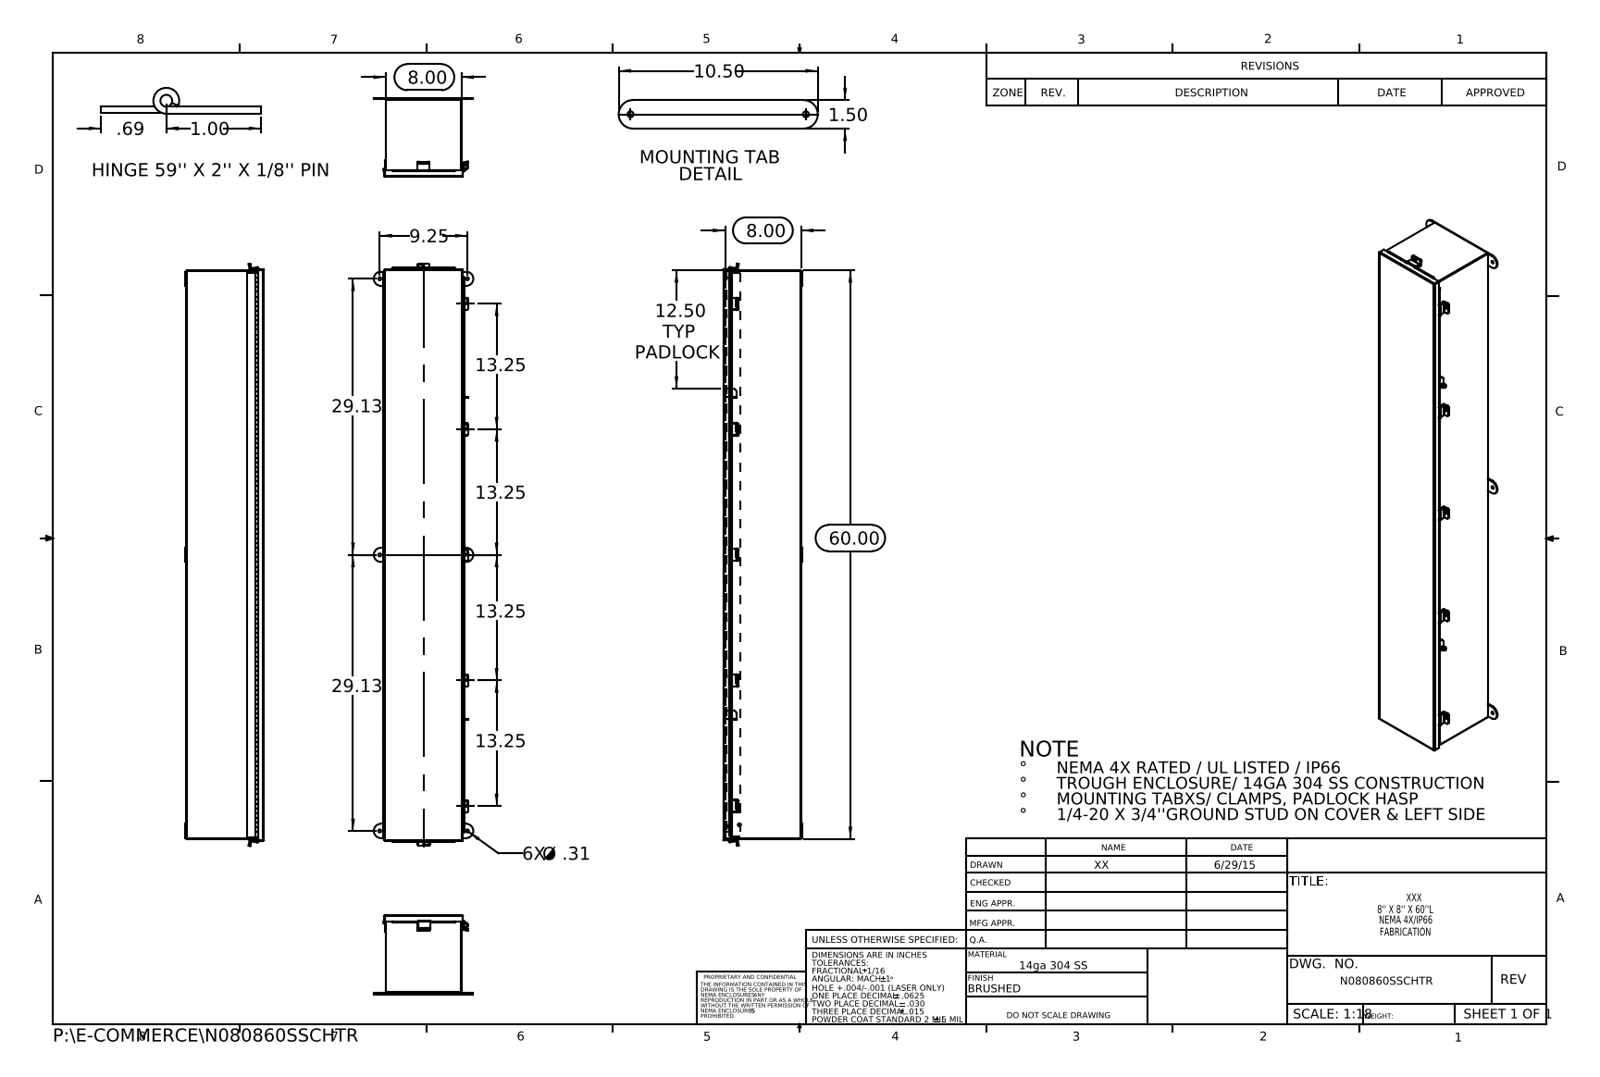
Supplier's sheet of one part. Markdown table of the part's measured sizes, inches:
| quantity | value |
| --- | --- |
| part name | N080860SSCHTR JIC_Cover_Template; N080860SSCHTR JIC Mounting Bracket; N080860SSCHTR JIC Clamp Bracket; HW-CLH-JH-20154 (+8 more) |
| STEP written by | SolidWorks 2015 (CONFIG_CONTROL_DESIGN) |
| units | inches |
| bodies | 27 solids, 1657 faces (986 planar, 651 cylindrical, 20 other) |
| overall size | 61.407 × 10.5 × 8.337 |
| volume | 179.4 in³ |
| surface area | 4 813 in² |
| round holes (diameter × count) | 0.25 × 7, 0.313 × 6, 0.125 × 1, 0.375 × 1 |
| round bosses / shafts (diameter × count) | 0.315 × 2, 0.236 × 2, 0.273 × 1, 0.25 × 1 |
| partial cylindrical surfaces (radius × count) | 0.125 × 27, 0.133 × 14, 0.009 × 12, 0.013 × 12, 0.088 × 12, 0.083 × 6, 0.1 × 6, 0.75 × 6 |
| main face-to-face distances | 0.075, 7.925, 8.128, 8, 7.85, 8.203, 8.053, 0.149, 8.074, 0.074 |
| hole center spacings | 13.25, 29.125, 30.559, 9.25, 26.5, 39.75, 58.25, 58.98 |
